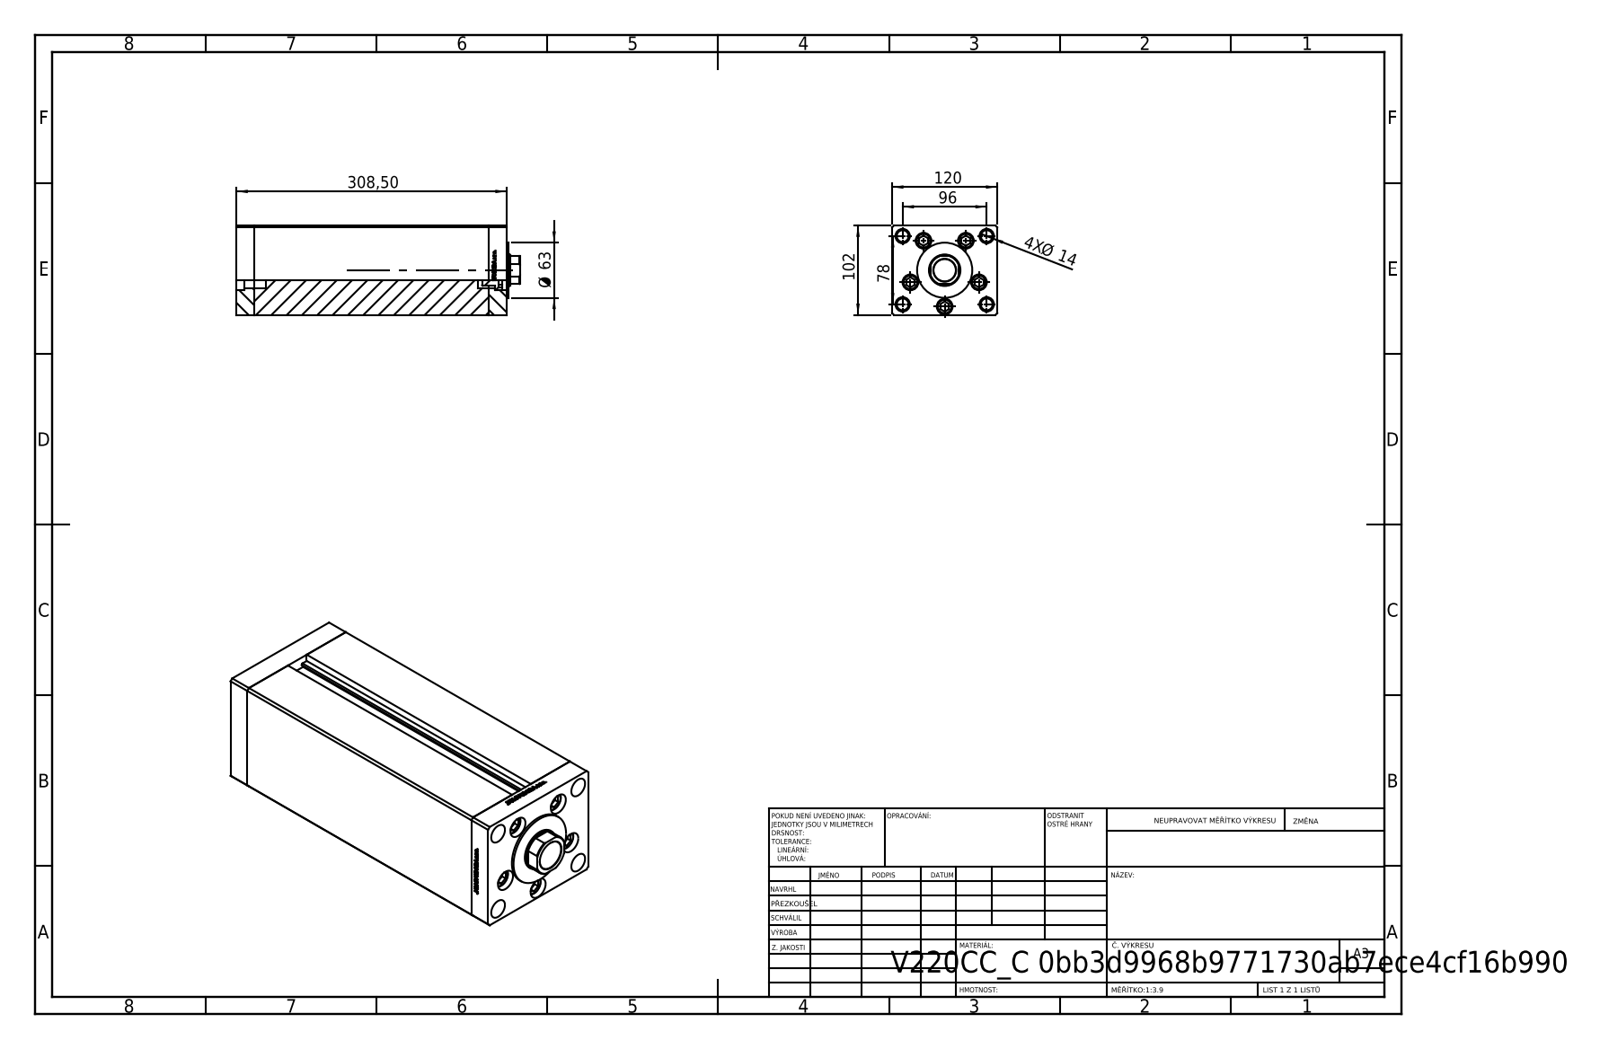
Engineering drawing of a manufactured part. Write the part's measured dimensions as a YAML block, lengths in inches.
part_name: "ALLEN BOLT; V220C_VC_C; V220C_C MIDDLE; V220C FRONT (+1 more)"
step_written_by: "SolidWorks 2019 (CONFIG_CONTROL_DESIGN)"
units: inches
bodies: {solids: 13, faces: 1165, planar: 542, cylindrical: 161, other: 462}
overall_size: [12.736, 4.724, 4.016]
volume: 191.3
surface_area: 582.7
round_holes:
  - {diameter: 0.531, count: 9}
  - {diameter: 0.709, count: 5}
  - {diameter: 0.472, count: 4}
  - {diameter: 0.65, count: 4}
  - {diameter: 0.669, count: 1}
  - {diameter: 1.004, count: 1}
  - {diameter: 1.417, count: 1}
round_bosses_or_shafts:
  - {diameter: 0.315, count: 5}
  - {diameter: 0.669, count: 4}
  - {diameter: 2.48, count: 1}
partial_cylinders:
  - {radius: 0.037, count: 2}
  - {radius: 0.689, count: 1}
face_to_face_distances: [4.724, 4.016, 0.787, 10.571, 11.358, 1.348, 12.146, 10.797, 10.01, 0.561]
hole_center_spacings: [1.634, 2.435, 0.96, 1.051, 1.887, 1.893, 1.962, 2.109]
